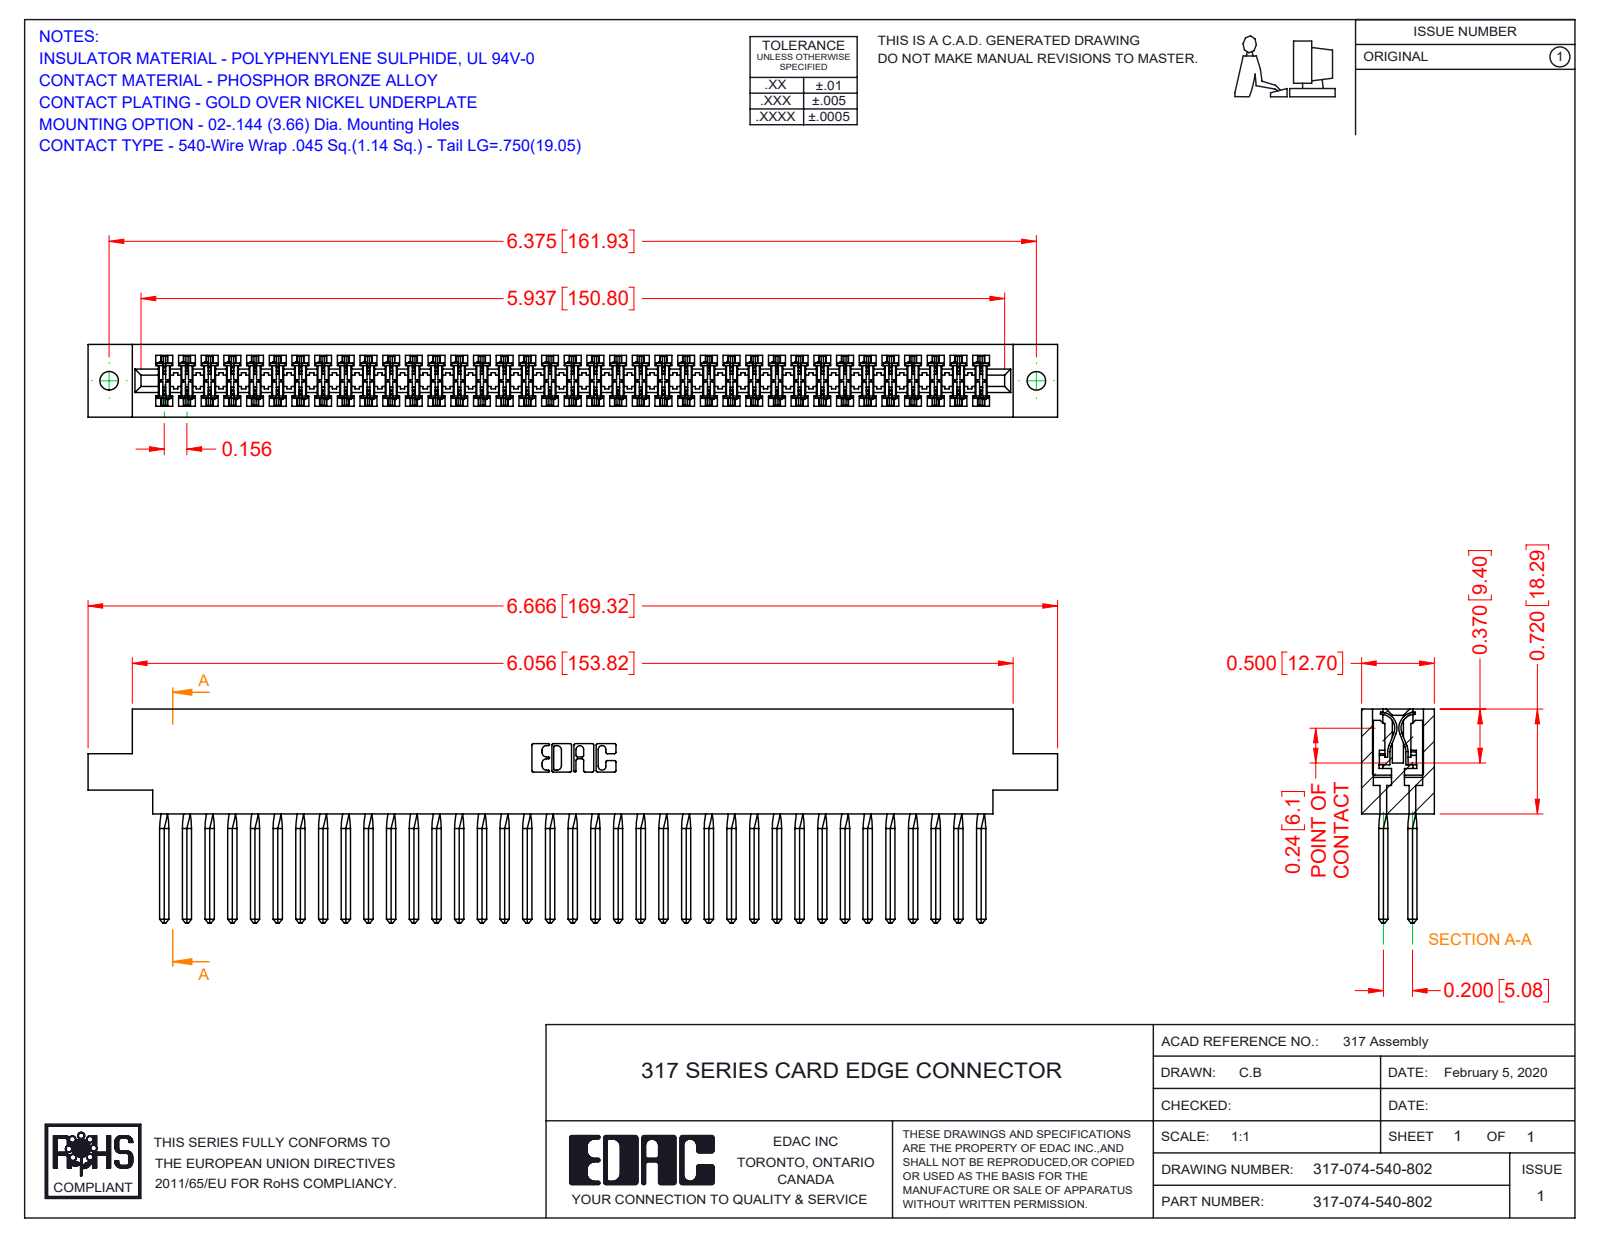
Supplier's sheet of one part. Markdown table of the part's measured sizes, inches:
| quantity | value |
| --- | --- |
| part name | 317-074-540-802; 317-290-001_540; 317 Part_.144 Dia |
| STEP written by | SolidWorks 2016 (CONFIG_CONTROL_DESIGN) |
| units | inches |
| bodies | 75 solids, 6688 faces (5460 planar, 932 cylindrical, 296 other) |
| overall size | 6.666 × 1.47 × 0.5 |
| volume | 1.722 in³ |
| surface area | 64.49 in² |
| round holes (diameter × count) | 0.128 × 2 |
| partial cylindrical surfaces (radius × count) | 0.015 × 148, 0.01 × 22, 0.007 × 6, 0.031 × 6, 0.026 × 3, 0.095 × 2, 0.1 × 2, 0.11 × 2 |
| main face-to-face distances | 0.5, 0.075, 0.425, 0.35, 0.195, 0.094, 0.11, 0.2, 0.115, 0.131 |
| hole center spacings | 6.375 |
